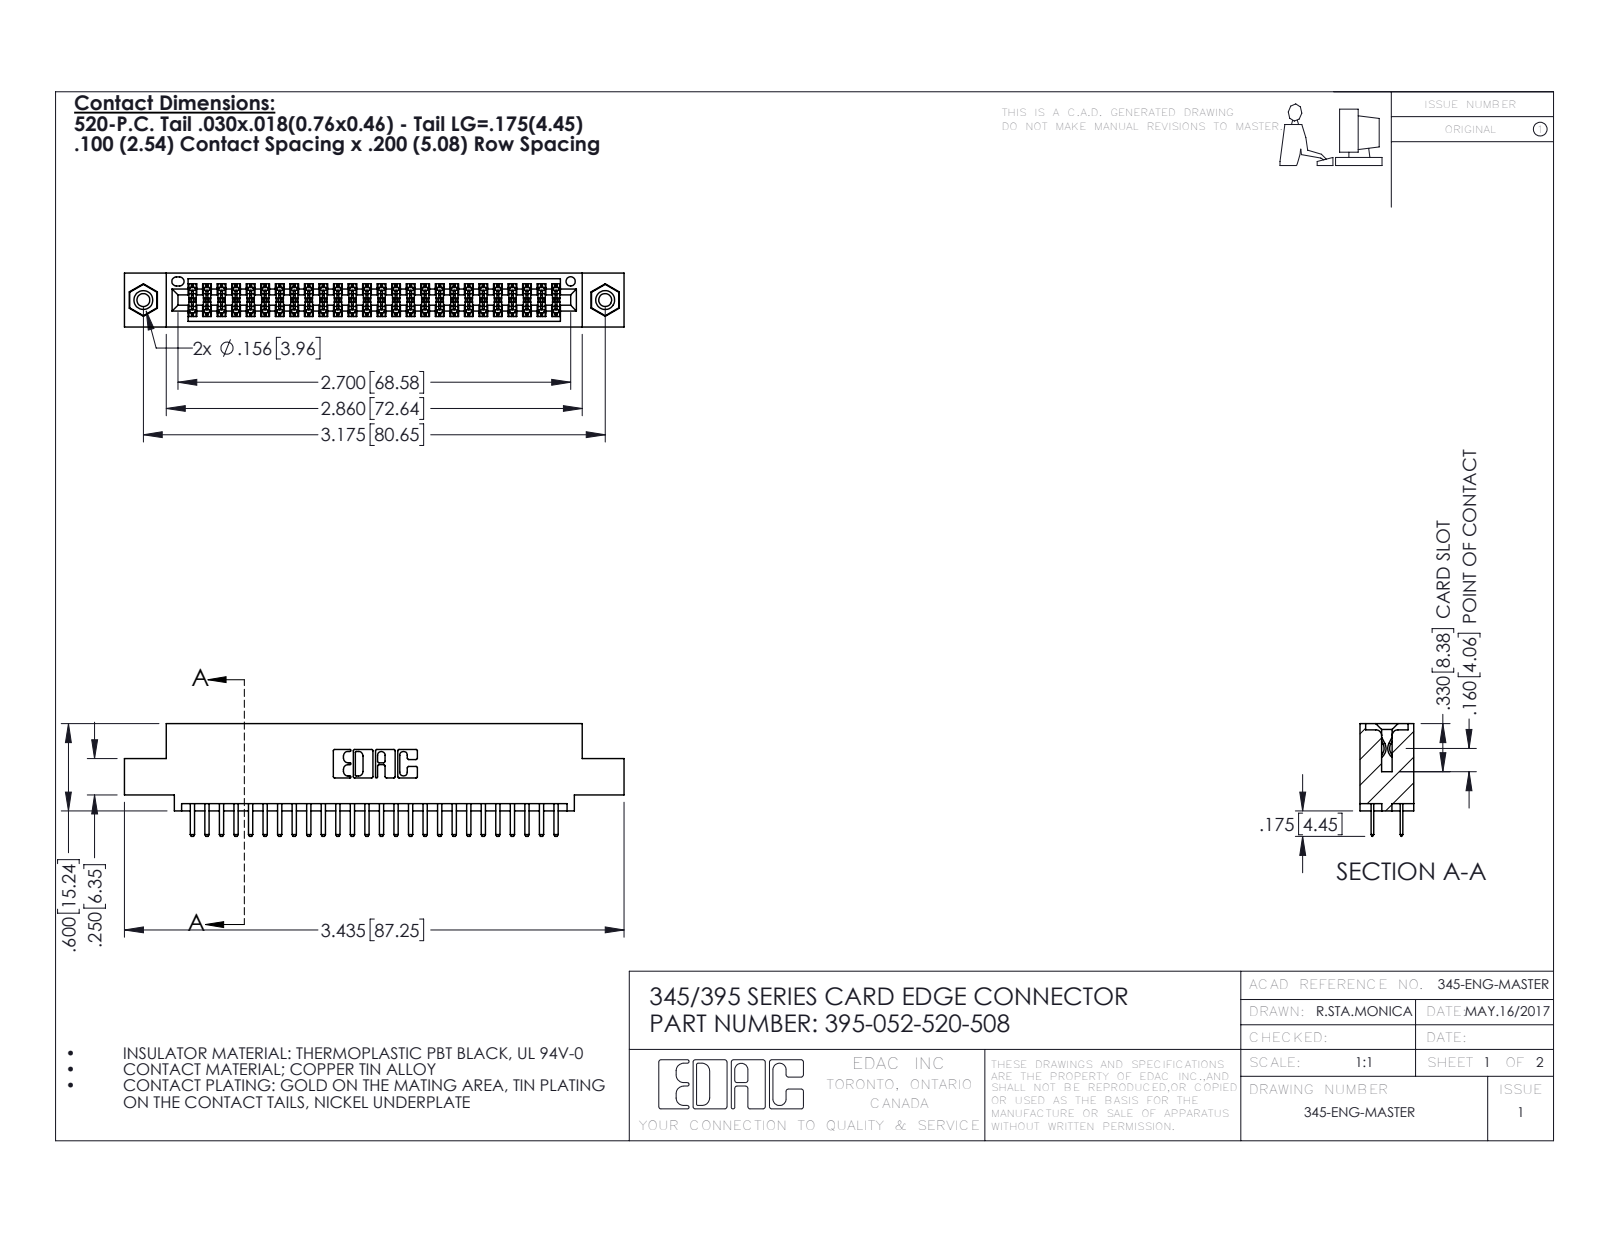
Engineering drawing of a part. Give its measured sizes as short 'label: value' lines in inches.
name: 345-250-001_345-250-003-102; 345-292-001_345-293-120; 345 Part_0.110 Offset - 0.156 Dia-TI; 395-052-520-508
written by: SolidWorks 2016 (CONFIG_CONTROL_DESIGN)
unit: in
bodies: 55 solids, 2998 faces (1936 planar, 1046 cylindrical, 16 other)
size: 3.435 × 0.775 × 0.37
volume: 0.502 in³; area: 18.45 in²
holes: 2× ⌀0.089, 2× ⌀0.125, 2× ⌀0.156, 1× ⌀0.064
bosses: 2× ⌀0.155
rounds: 78× R0.006, 56× R0.01, 22× R0.01, 6× R0.007, 6× R0.031, 3× R0.026, 2× R0.014, 2× R0.019
face distances: 0.072, 0.298, 0.2, 0.37, 0.098, 0.272, 0.025, 0.225, 0.022, 0.072
hole spacings: 0.27, 2.94, 3.175
